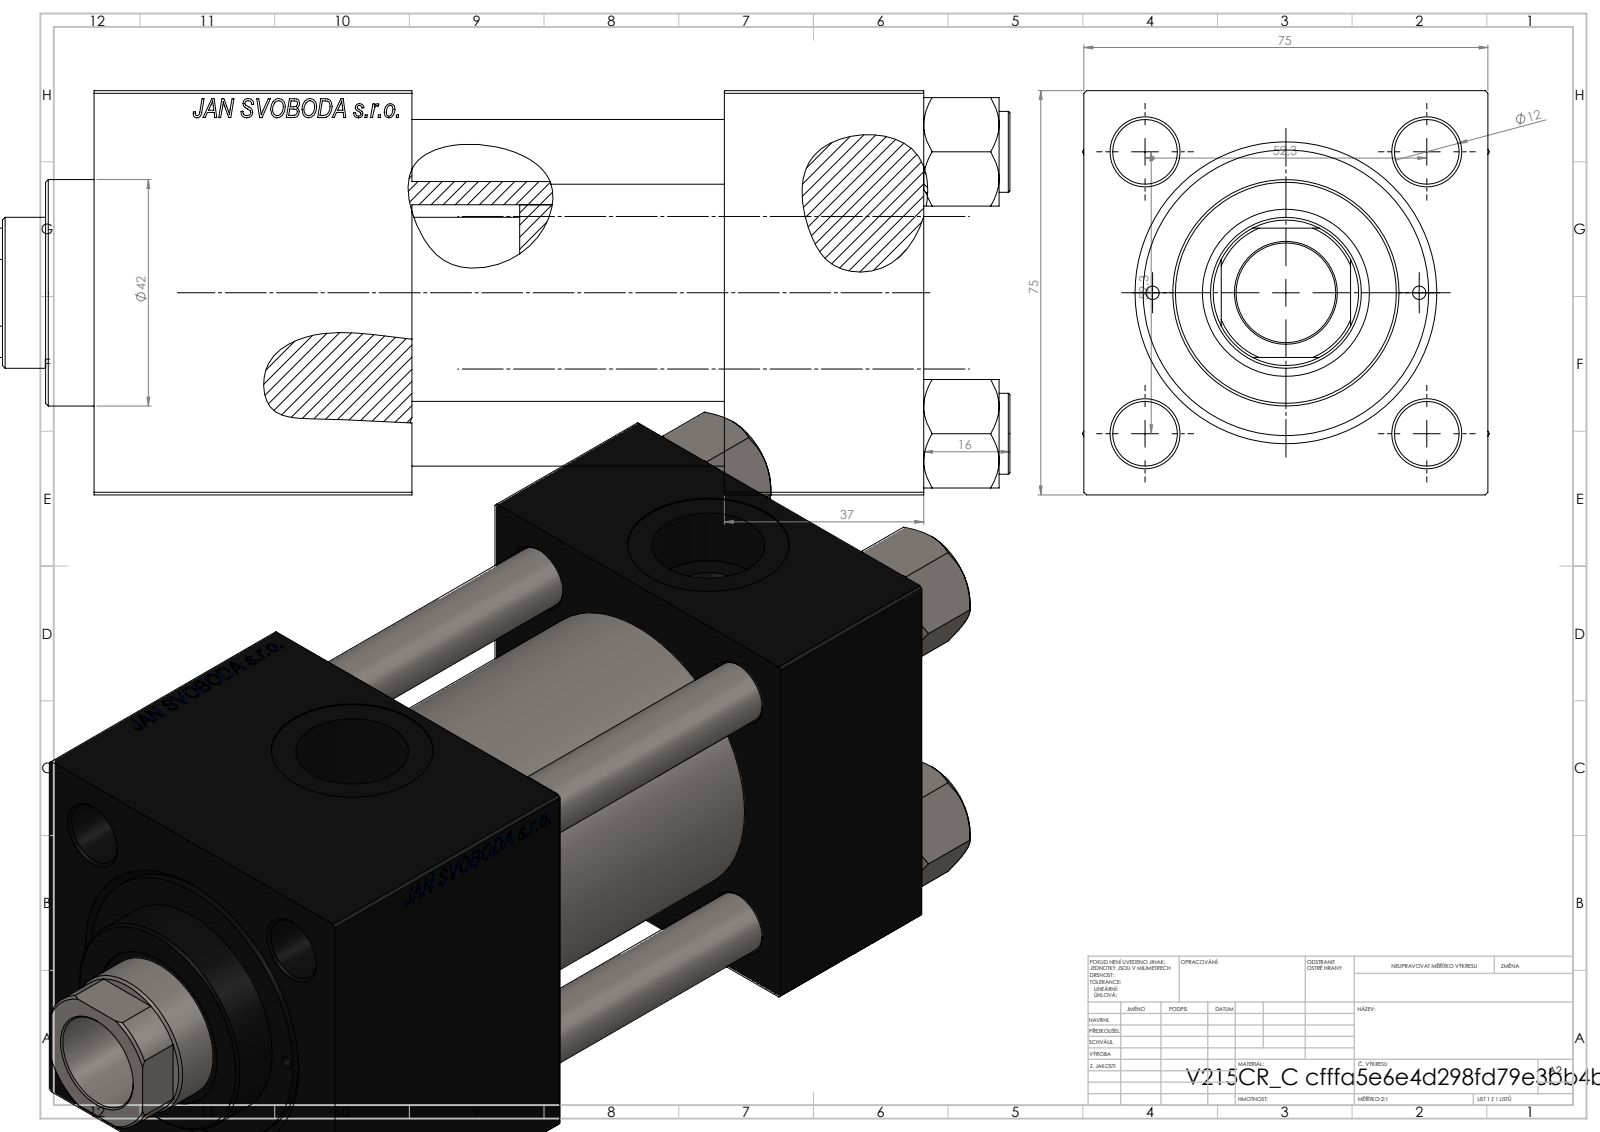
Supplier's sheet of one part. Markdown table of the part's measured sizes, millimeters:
| quantity | value |
| --- | --- |
| part name | V215CR_C_Body; NUT_M5_C; V215_VC_A; V215CR_VCP_C (+1 more) |
| STEP written by | SolidWorks 2019 (CONFIG_CONTROL_DESIGN) |
| units | millimeters |
| bodies | 11 solids, 1155 faces (528 planar, 91 cylindrical, 536 other) |
| overall size | 195 × 75.54 × 75 |
| volume | 668 914 mm³ |
| surface area | 151 016 mm² |
| round holes (diameter × count) | 12 × 4, 2.5 × 2, 7 × 2, 20.96 × 2, 30 × 2, 18.5 × 1, 28 × 1, 31 × 1, 41 × 1, 50 × 1, 53 × 1 |
| round bosses / shafts (diameter × count) | 15 × 4, 56 × 1, 42 × 1 |
| partial cylindrical surfaces (radius × count) | 13.5 × 1 |
| main face-to-face distances | 75, 37, 154, 117, 59, 95, 58, 125.3, 88.3, 30.3 |
| hole center spacings | 26.19, 36.98, 52.3, 57.22, 24.75, 73.96, 49.5, 93.5 |
